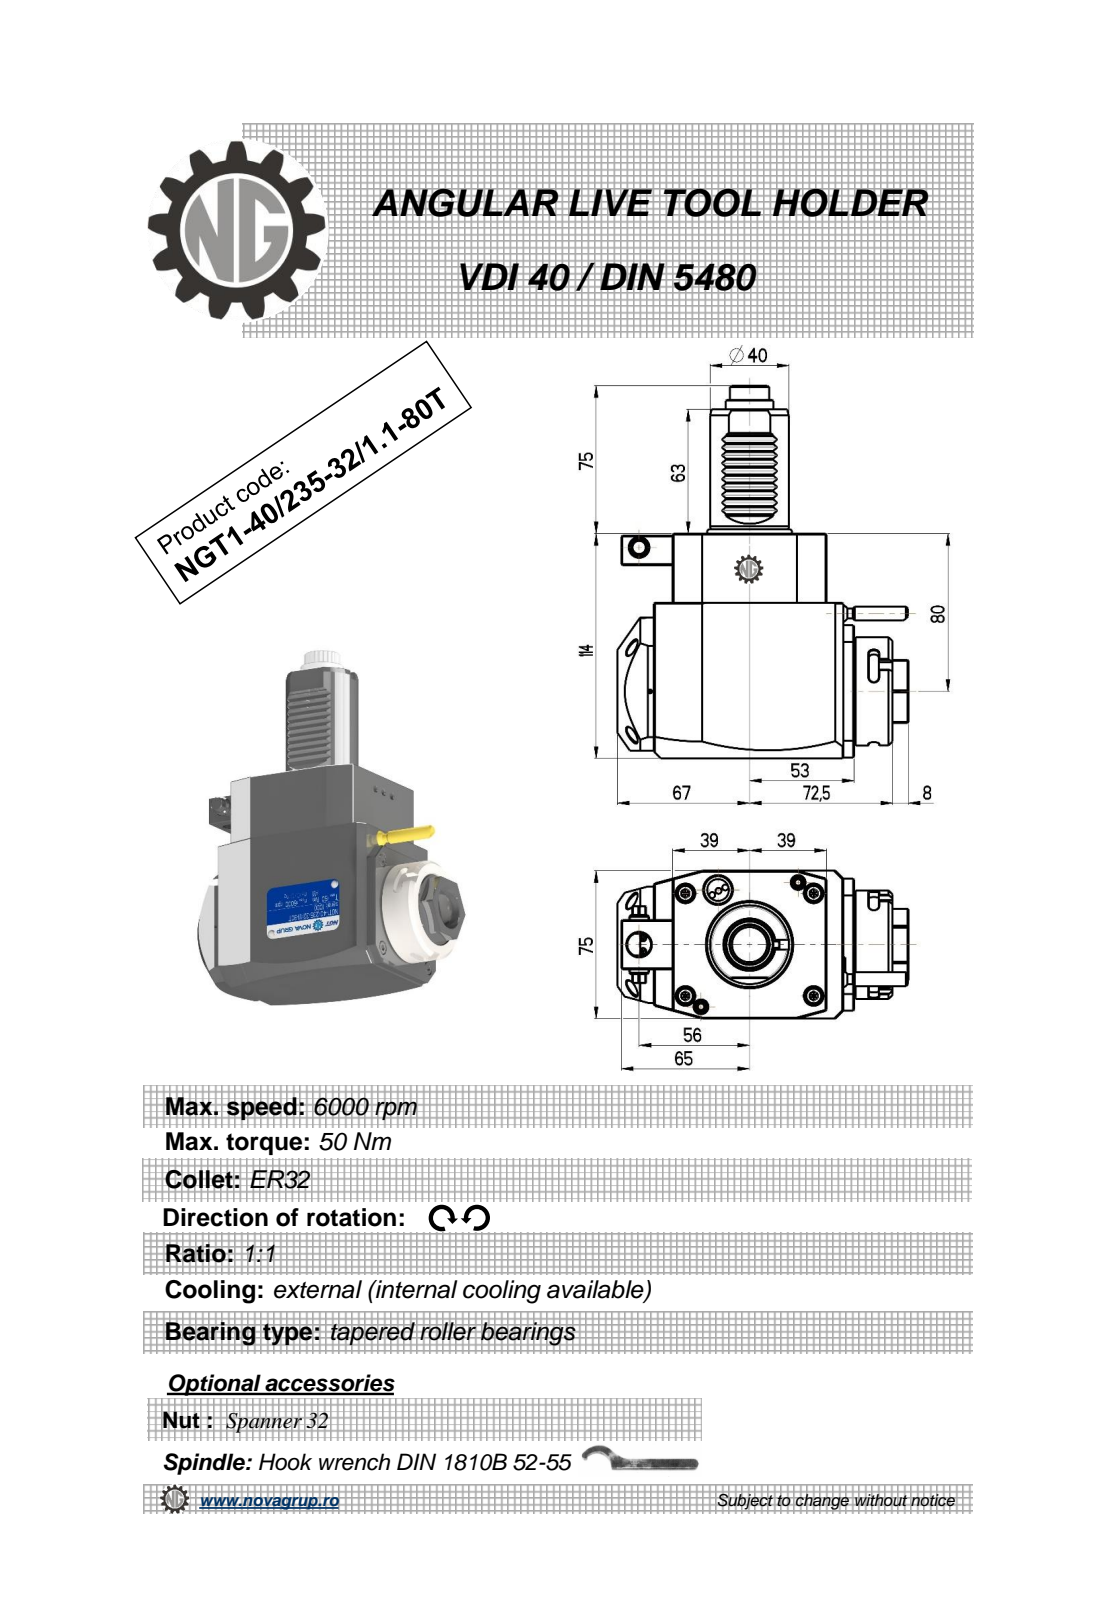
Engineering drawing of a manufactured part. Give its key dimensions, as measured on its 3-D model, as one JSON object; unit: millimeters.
{"part_name": "NGT1_40_235_32_1_1_80T", "step_written_by": "PRO/ENGINEER BY PARAMETRIC TECHNOLOGY CORPORATION, 2010280 (CONFIG_CONTROL_DESIGN)", "units": "millimeters", "bodies": {"solids": 1, "faces": 458, "planar": 192, "cylindrical": 172, "other": 94}, "overall_size": [189, 147.5, 75], "volume_mm3": 965747, "surface_area_mm2": 72046, "round_holes": [[2.5, 1], [3, 1], [9.5, 1], [12, 1], [23, 1]], "round_bosses_or_shafts": [[8, 2], [55, 1], [48, 1], [40, 1], [24, 1], [10, 1], [7, 1], [5, 1]], "partial_cylinders_radius": [[2.08, 48], [0.3, 10], [2.5, 6], [180, 2], [3.85, 1], [4.25, 1], [9.08, 1], [9.92, 1]], "face_to_face_distances": [75, 114, 14, 78, 92, 79, 25, 19.5, 111.5, 33.5], "hole_center_spacings": [36.47, 43.2, 71.5]}
